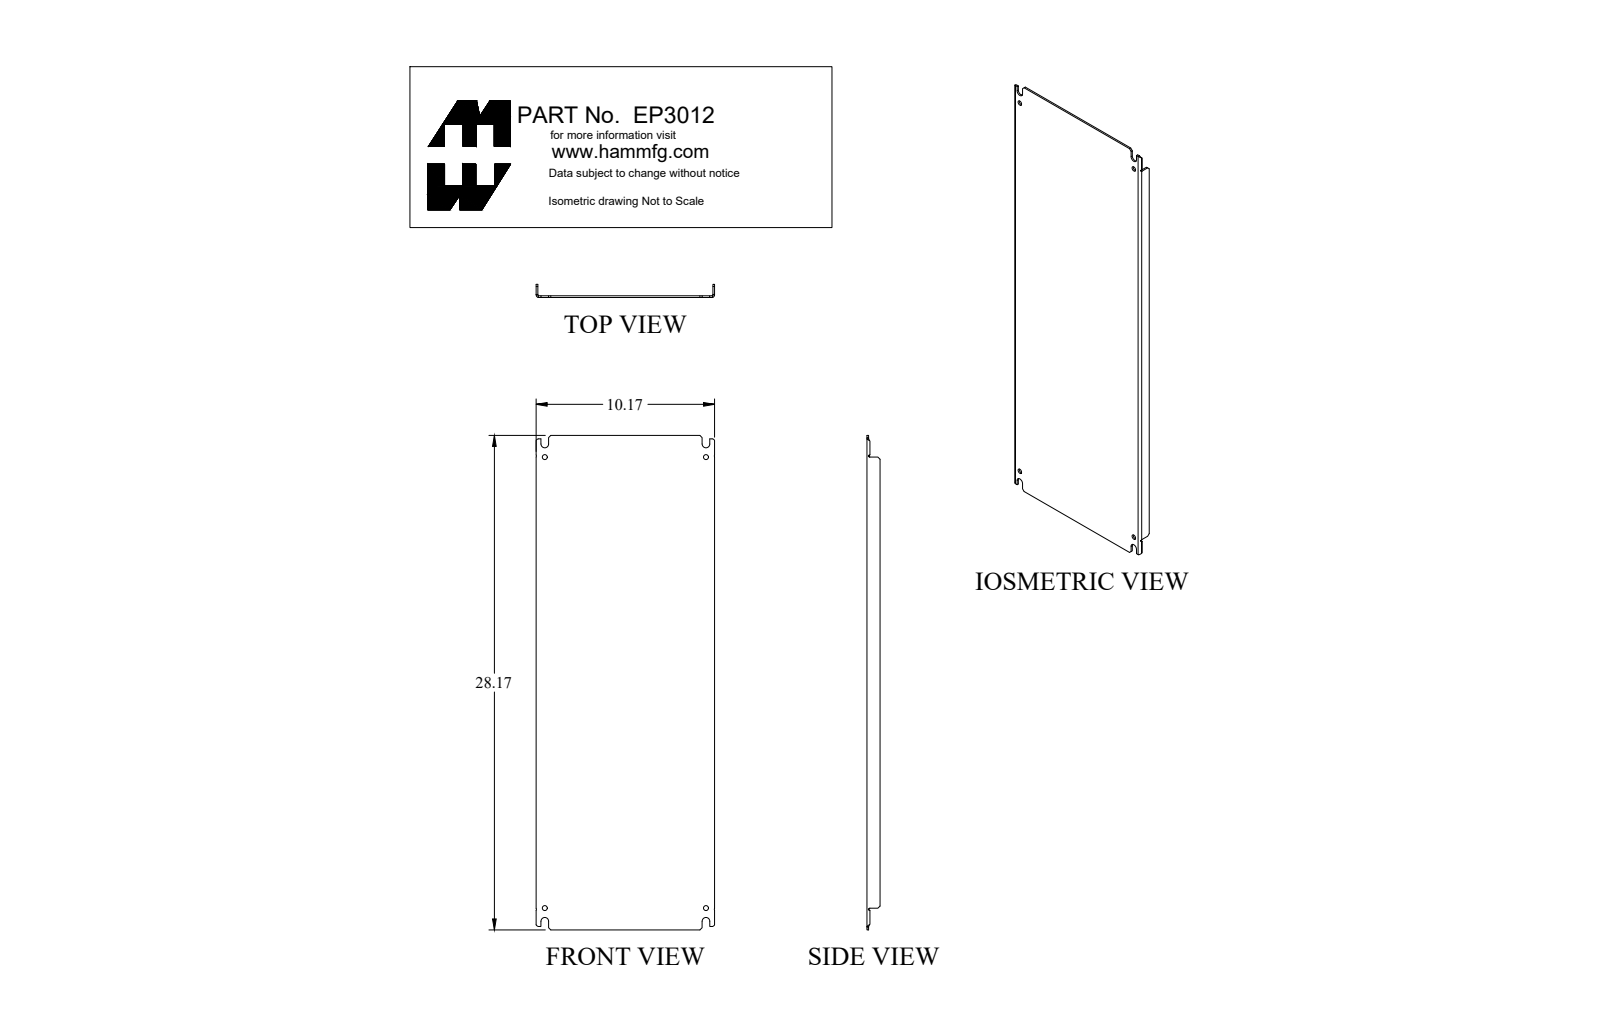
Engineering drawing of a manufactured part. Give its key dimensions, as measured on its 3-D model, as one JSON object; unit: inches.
{"part_name": "EP3012", "step_written_by": "SolidWorks 2018 (AUTOMOTIVE_DESIGN)", "units": "inches", "bodies": {"solids": 1, "faces": 84, "planar": 50, "cylindrical": 26, "other": 8}, "overall_size": [28.17, 10.17, 0.75], "volume_in3": 30.06, "surface_area_in2": 641, "round_holes": [[0.281, 4]], "partial_cylinders_radius": [[0.219, 4], [0.048, 2], [0.062, 2], [0.143, 2]], "face_to_face_distances": [0.095, 10.075, 9.98, 10.17, 0.75, 0.655, 28.17, 0.171, 0.076, 0.579], "hole_center_spacings": [9.188, 25.688, 27.282]}
